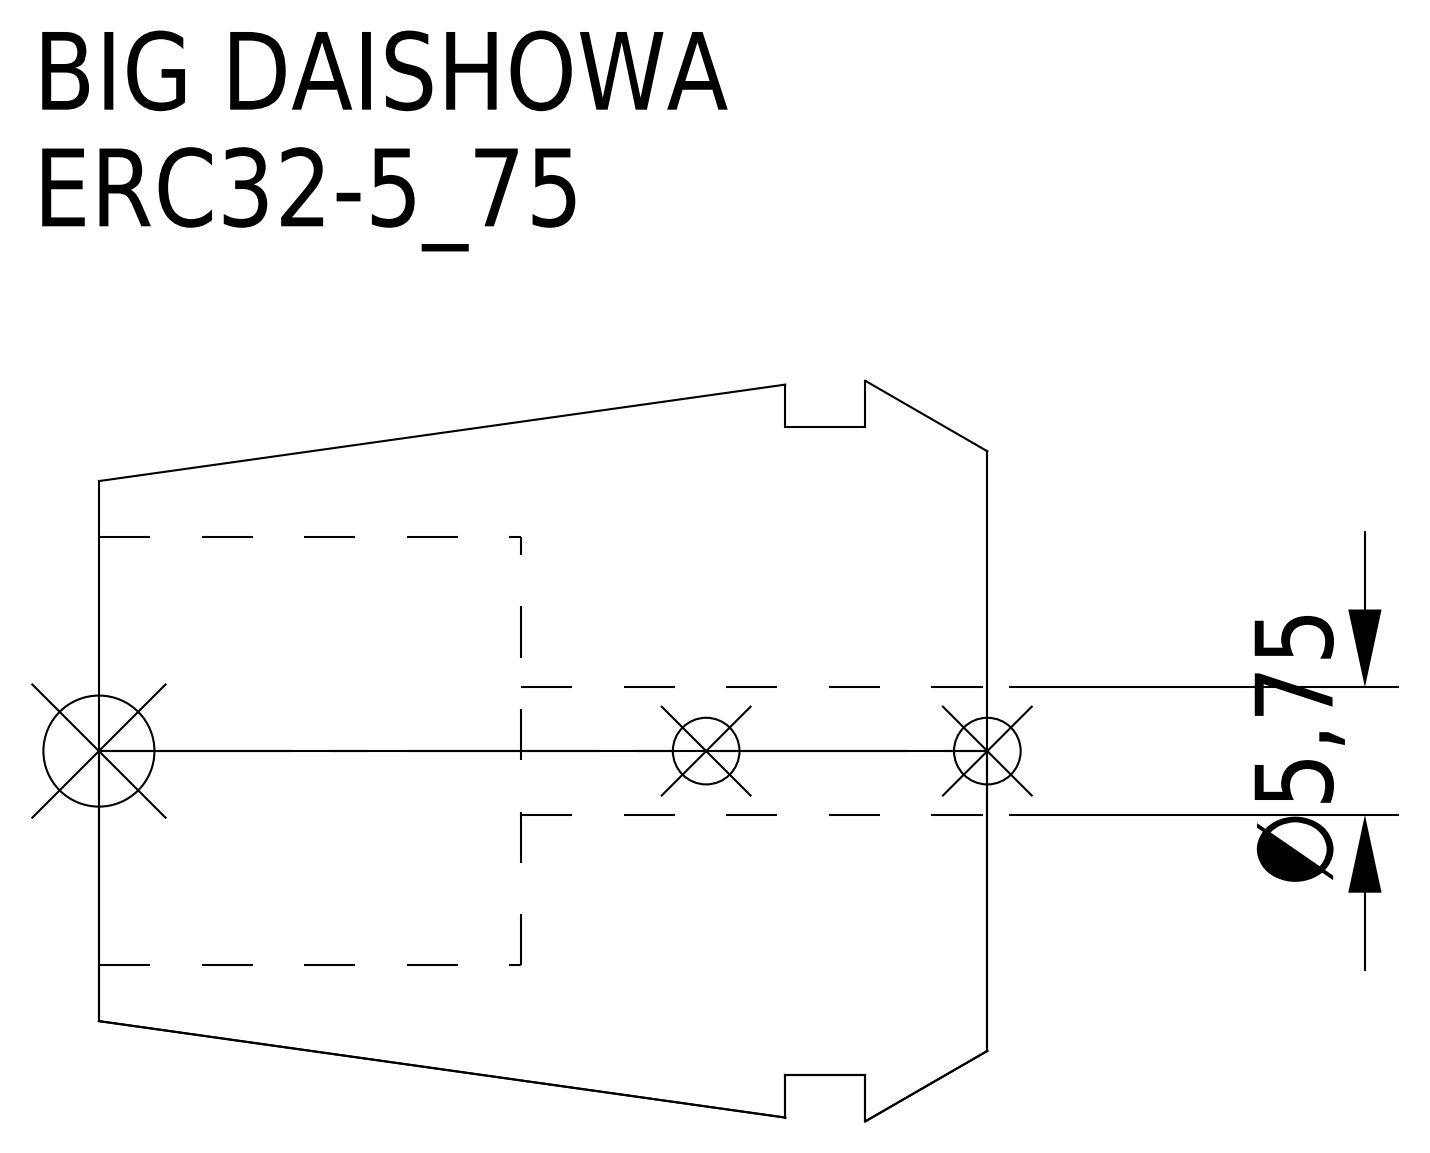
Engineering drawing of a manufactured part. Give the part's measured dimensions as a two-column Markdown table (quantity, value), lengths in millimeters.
| quantity | value |
| --- | --- |
| part name | ERC32-5_75 |
| STEP written by | CREO PARAMETRIC BY PTC INC, 2016380 (AUTOMOTIVE_DESIGN) |
| units | millimeters |
| bodies | 1 solid, 15 faces (5 planar, 6 cylindrical, 4 other) |
| overall size | 40 × 33.35 × 33.35 |
| volume | 20 339 mm³ |
| surface area | 6 647 mm² |
| round holes (diameter × count) | 5.75 × 1, 19.3 × 1 |
| round bosses / shafts (diameter × count) | 29.2 × 1 |
| main face-to-face distances | 21, 5.5, 15.5, 9.1, 3.6, 11.9, 40, 34.5, 30.9, 19 |
